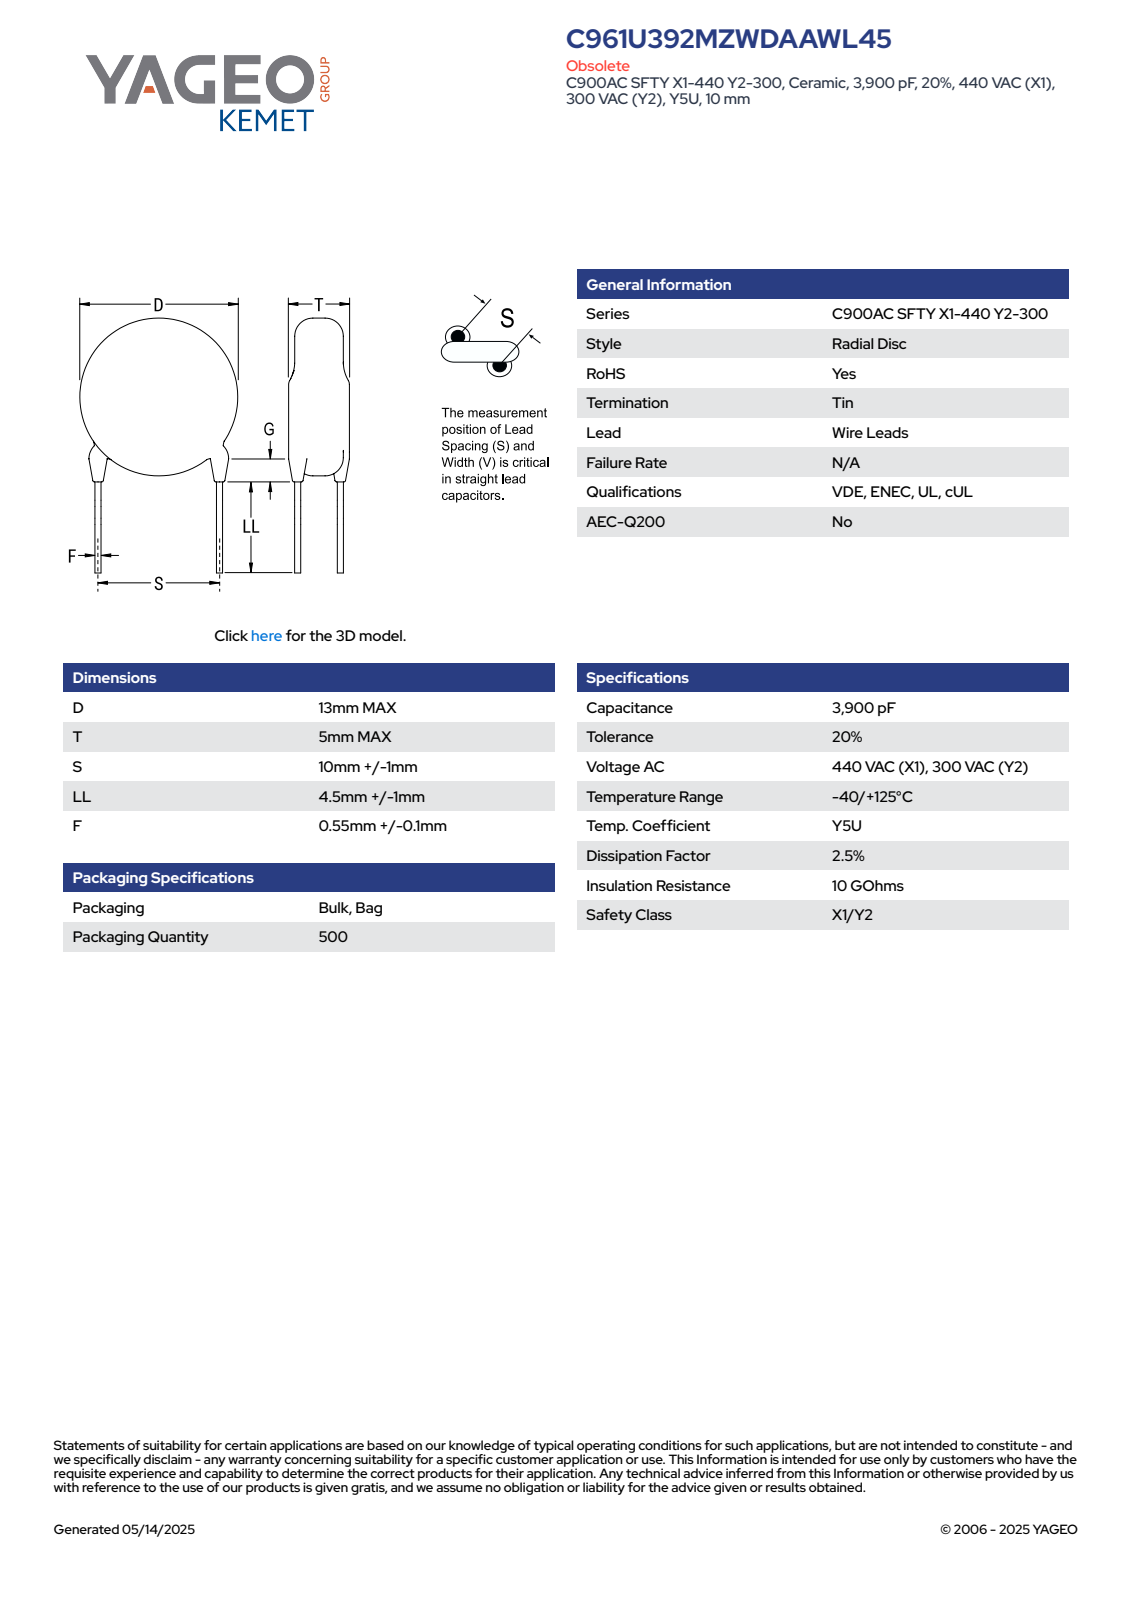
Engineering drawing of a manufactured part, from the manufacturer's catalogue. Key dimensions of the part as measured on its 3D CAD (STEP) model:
Part name (STEP PRODUCT): CCD_STC900_D13T5S10LL5.5F0.65G3
STEP written by: SolidWorks 2014 (AUTOMOTIVE_DESIGN)
Units: millimetres
Bodies: 4 solids, 83 faces (61 planar, 6 cylindrical, 16 other)
Overall size (bounding box): 18.81 × 13 × 5
Volume: 654 mm³ · Surface area: 480 mm²
Round bosses / shafts (diameter × count): ⌀0.65 ×2, ⌀13 ×1
Main face-to-face distances: 5, 1.5, 13.06, 11.56, 0.41, 6.13, 0.93, 3.1, 4.45, 4.63
